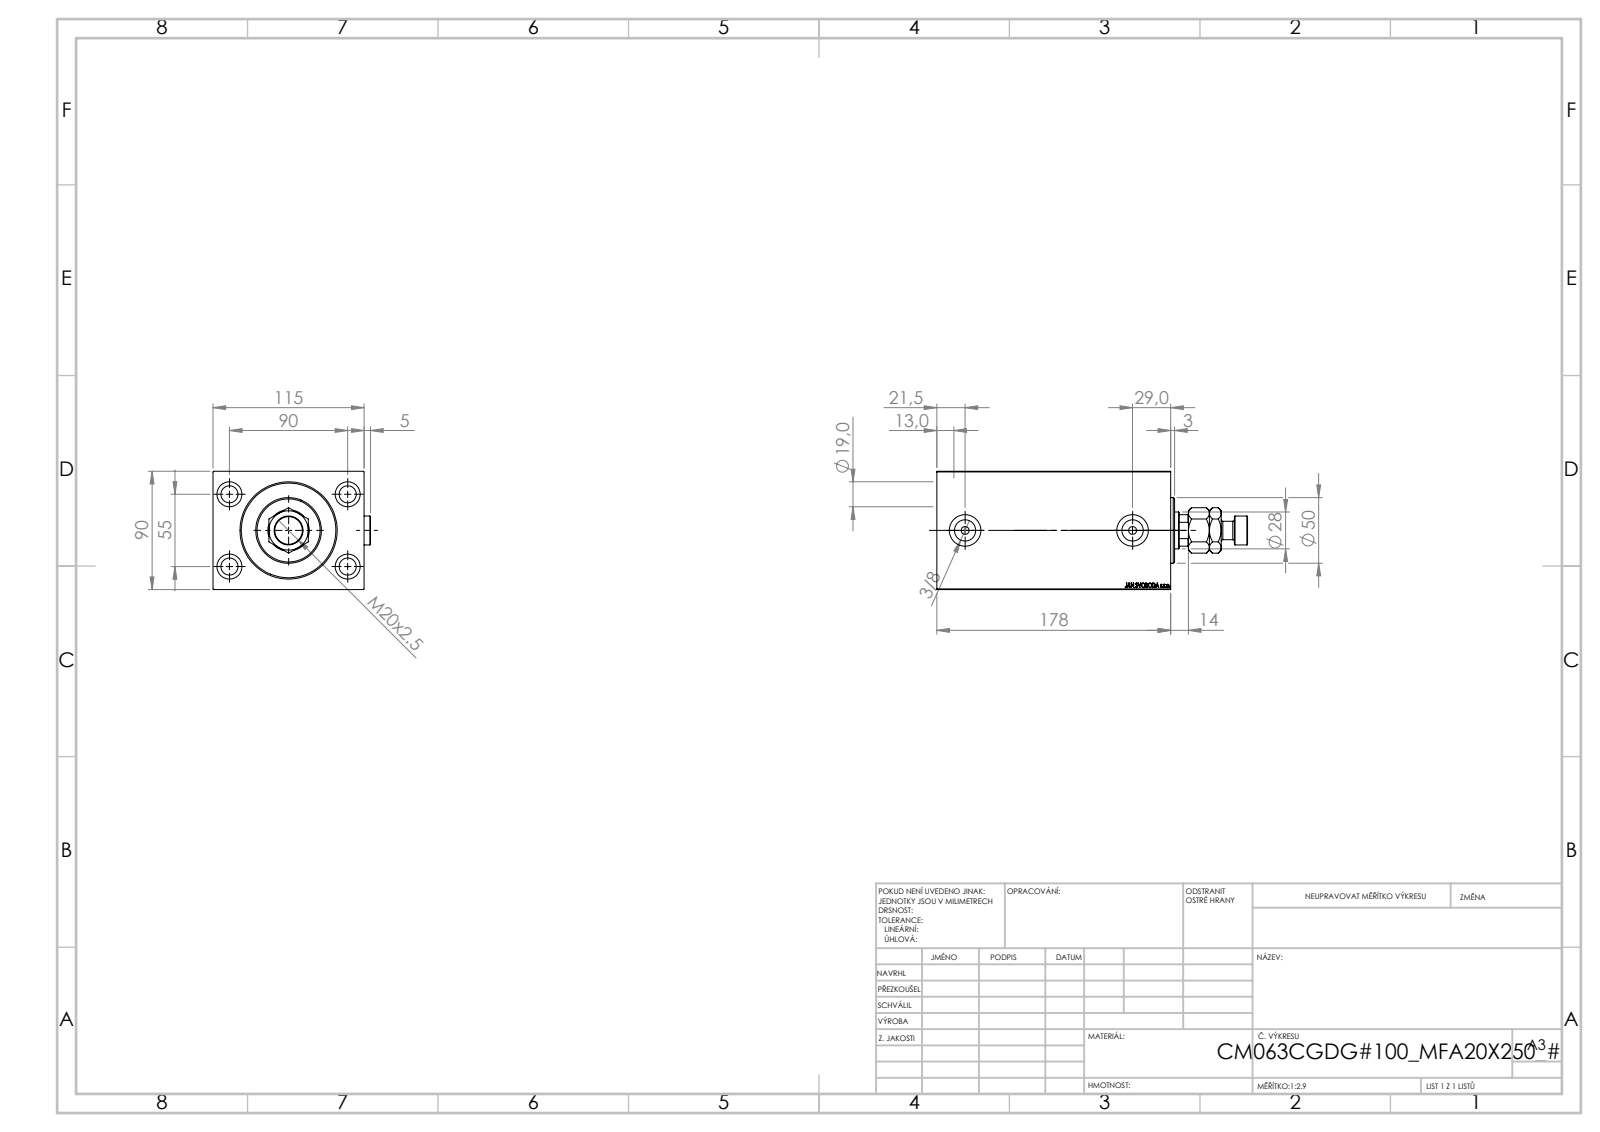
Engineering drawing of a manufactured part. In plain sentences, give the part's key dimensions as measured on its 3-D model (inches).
The part is named "V450CM_VC_B; Zatka_OIL_PORT; MFA; V450CM_C_Body (+1 more)". Its 3-D file was written by "SolidWorks 2019 (CONFIG_CONTROL_DESIGN)". It is 6 solids with 971 faces: 459 planar, 82 cylindrical and 430 other. Overall it measures 9.311 by 4.72 by 3.543 inches. Its volume is 91.66 cubic inches and its surface area 320.1 square inches. Round holes: 4 of diameter 0.512, 4 of diameter 0.748, 2 of diameter 0.236, 2 of diameter 0.637, 2 of diameter 0.945, 1 of diameter 0.728, 1 of diameter 1.102, 1 of diameter 1.24, 1 of diameter 2.48, 1 of diameter 2.559, 1 of diameter 2.835. Round bosses or shafts: 3 of diameter 0.866, 1 of diameter 1.969, 1 of diameter 0.551. Partial cylindrical surfaces (rounded edges, fillets, slot ends): 1 of radius 0.531. The main face-to-face distances are 3.543, 4.528, 7.008, 0.689, 6.319, 0.531, 5.787, 6.476, 1.85, 4.469. The hole center spacings are 2.076, 2.165, 3.543, 4.153, 5.02.
